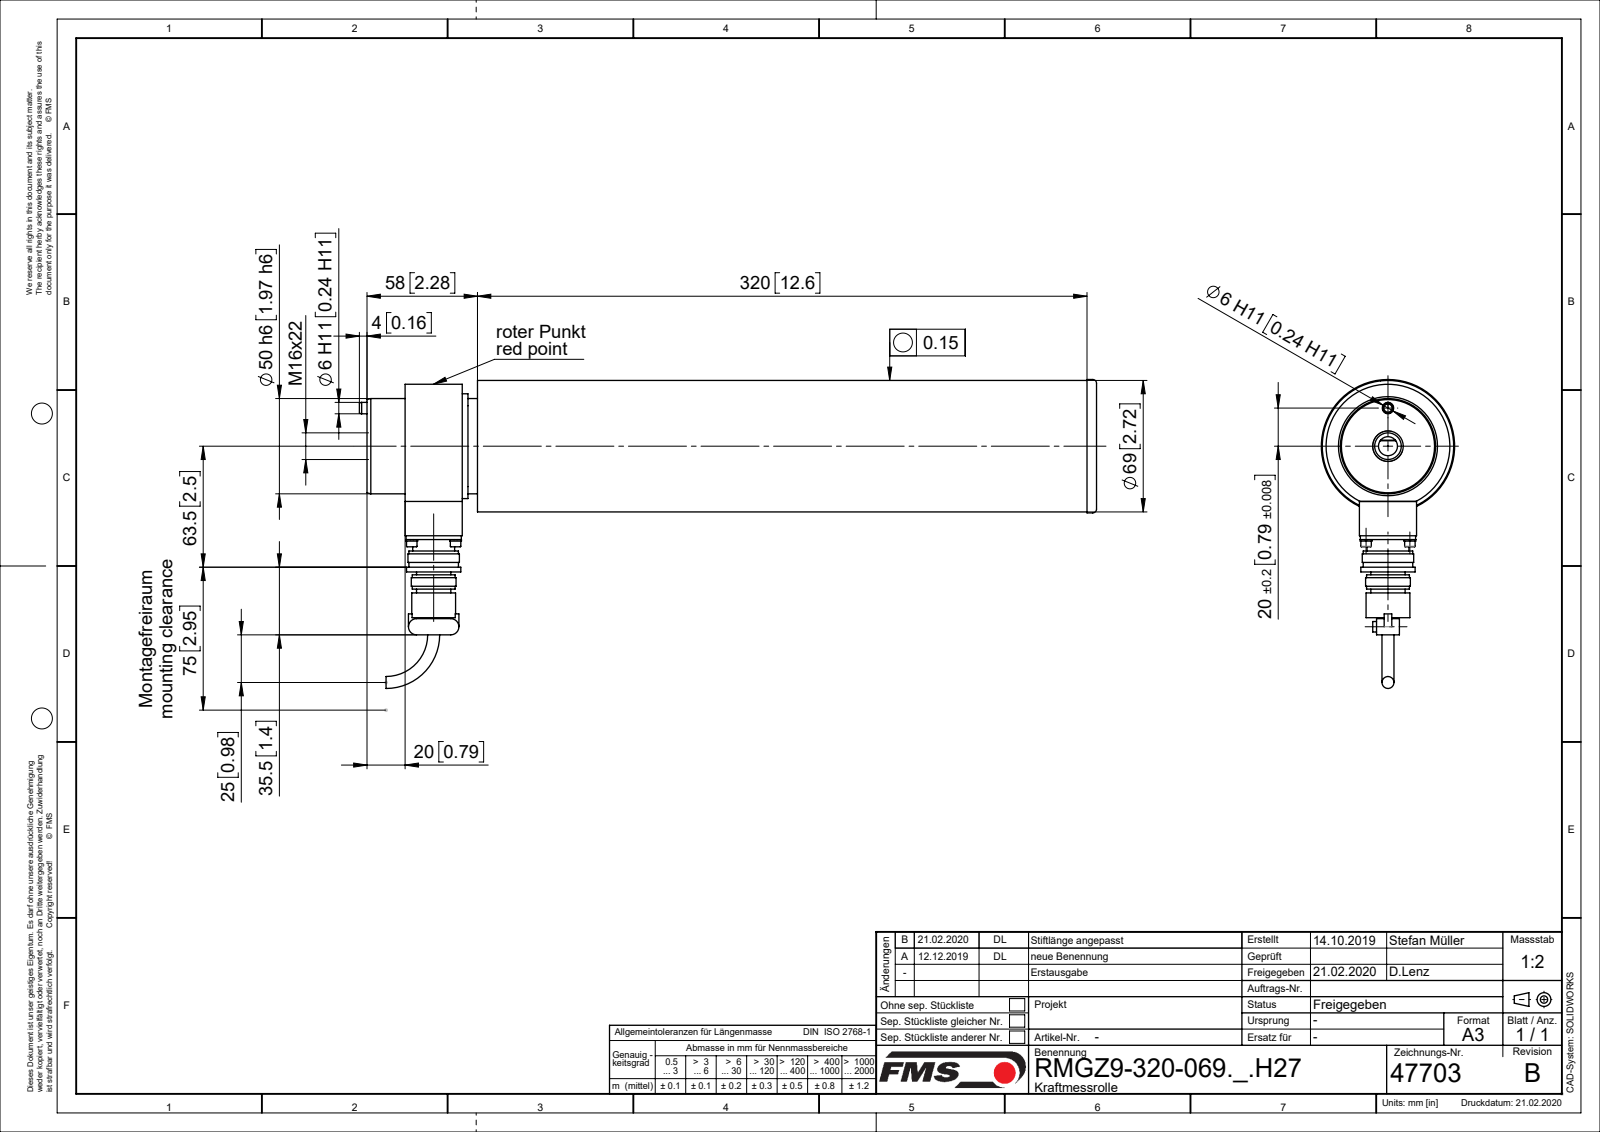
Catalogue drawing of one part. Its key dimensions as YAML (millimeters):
part_name: "49026_01; 47708_H15; 51460_01; Spannstift_ISO13337_D06x12 (+8 more)"
step_written_by: "SolidWorks 2018 (CONFIG_CONTROL_DESIGN)"
units: millimeters
bodies: {solids: 31, faces: 597, planar: 172, cylindrical: 259, other: 166}
overall_size: [387, 162.15, 70]
volume: 804072
surface_area: 272746
round_holes:
  - {diameter: 2.5, count: 6}
  - {diameter: 3.1, count: 4}
  - {diameter: 3.4, count: 4}
  - {diameter: 3.3, count: 1}
  - {diameter: 5, count: 1}
  - {diameter: 6, count: 1}
  - {diameter: 10, count: 1}
  - {diameter: 12, count: 1}
  - {diameter: 14, count: 1}
  - {diameter: 17, count: 1}
  - {diameter: 22, count: 1}
  - {diameter: 23, count: 1}
round_bosses_or_shafts:
  - {diameter: 5.5, count: 6}
  - {diameter: 6.2, count: 4}
  - {diameter: 3, count: 4}
  - {diameter: 2.5, count: 4}
  - {diameter: 70, count: 1}
  - {diameter: 69, count: 1}
  - {diameter: 65, count: 1}
  - {diameter: 58, count: 1}
partial_cylinders:
  - {radius: 0.1, count: 4}
  - {radius: 11, count: 4}
  - {radius: 4.19, count: 2}
  - {radius: 4.25, count: 2}
  - {radius: 17.5, count: 1}
  - {radius: 22.2, count: 1}
  - {radius: 25.37, count: 1}
face_to_face_distances: [50, 35, 328, 330, 3, 2, 53, 5, 38, 20]
hole_center_spacings: [16.26, 23, 24.85, 32.53, 18.14, 20, 25.59, 37.16]
